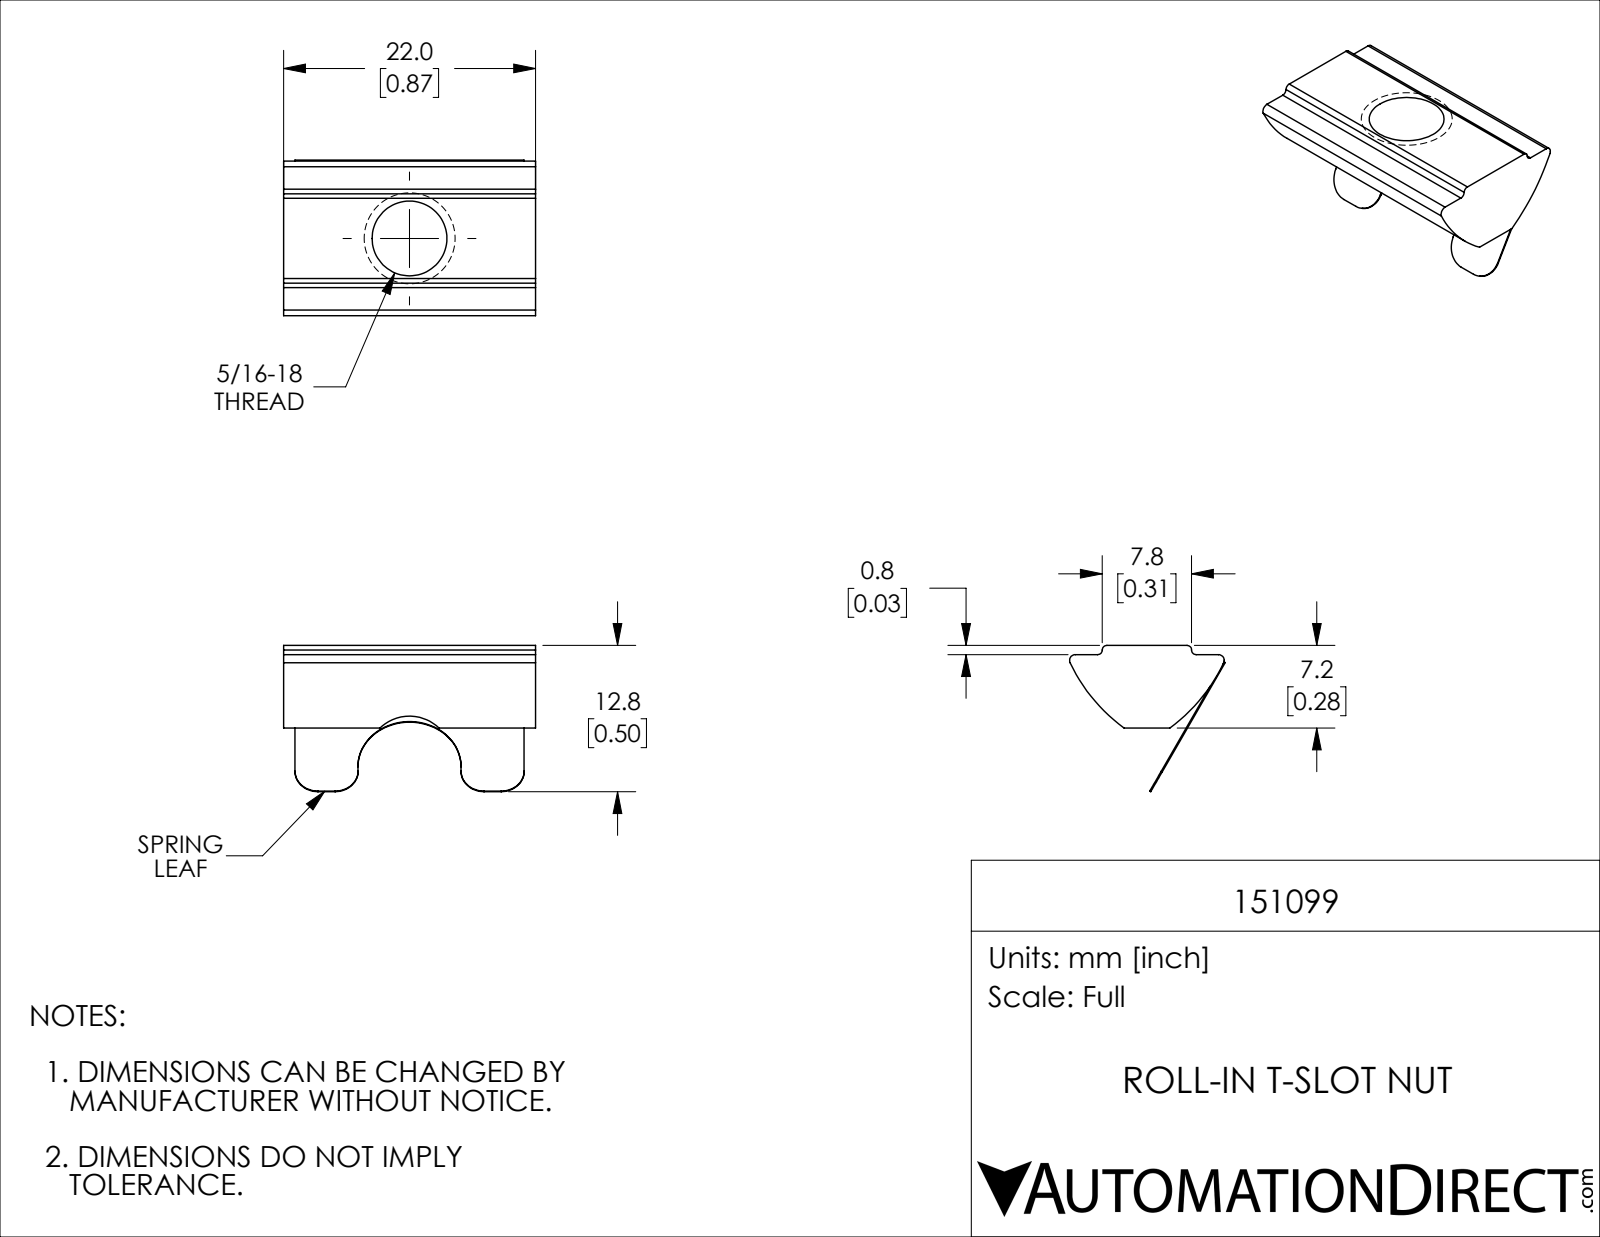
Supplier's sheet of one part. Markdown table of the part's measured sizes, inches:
| quantity | value |
| --- | --- |
| part name | 151099 |
| STEP written by | SolidWorks 2021 (CONFIG_CONTROL_DESIGN) |
| units | inches |
| bodies | 1 solid, 33 faces (17 planar, 16 cylindrical, 0 other) |
| overall size | 0.866 × 0.535 × 0.502 |
| volume | 0.08 in³ |
| surface area | 2 in² |
| round holes (diameter × count) | 0.257 × 1 |
| partial cylindrical surfaces (radius × count) | 0.016 × 4, 0.079 × 4, 0.02 × 2, 0.591 × 2, 0.177 × 1 |
| main face-to-face distances | 0.031, 0.866, 0.252, 0.283, 0.039, 0.827, 0.787, 0.512, 0.256, 0.61 |
